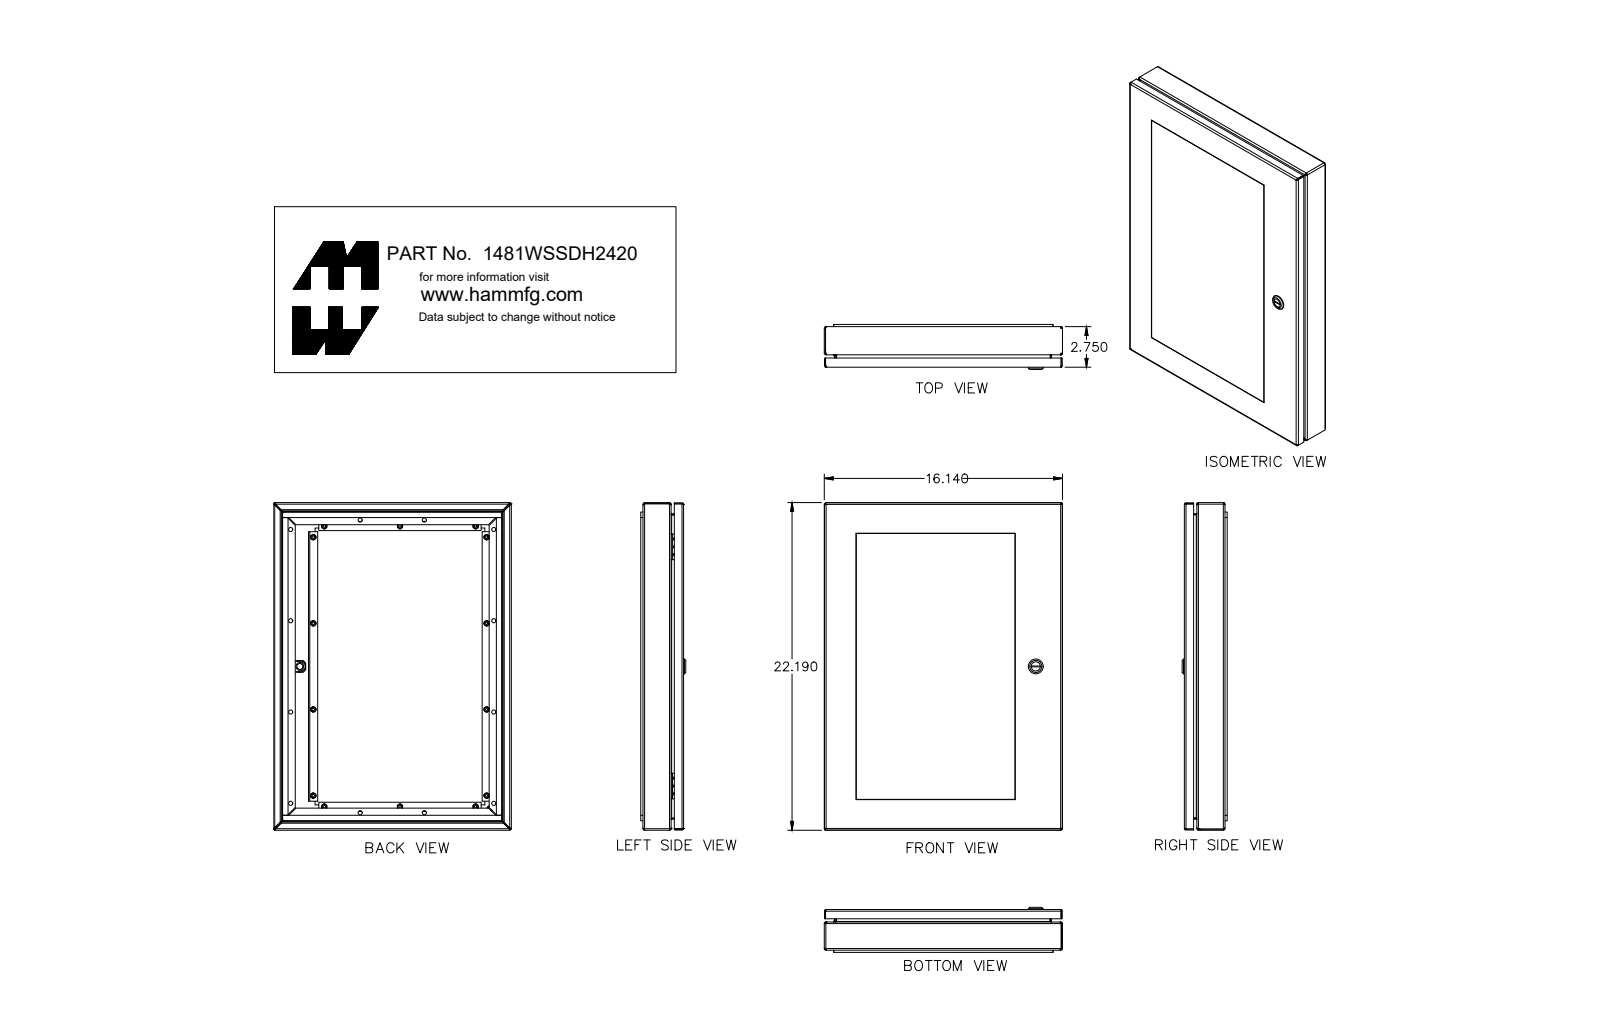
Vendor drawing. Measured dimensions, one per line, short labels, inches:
name: 1481WSSDH2420_Default
written by: SolidWorks 2019 (CONFIG_CONTROL_DESIGN)
unit: in
bodies: 50 solids, 1155 faces (617 planar, 334 cylindrical, 204 other)
size: 22.19 × 16.14 × 2.91
volume: 94.57 in³; area: 1 701 in²
holes: 14× ⌀0.13, 12× ⌀0.281, 2× ⌀0.136, 1× ⌀0.197, 1× ⌀0.24, 1× ⌀0.242, 1× ⌀0.387, 1× ⌀0.5, 1× ⌀0.63, 1× ⌀0.768
bosses: 14× ⌀0.368, 14× ⌀0.226, 14× ⌀0.164, 1× ⌀1.1, 1× ⌀0.785, 1× ⌀0.625, 1× ⌀0.525, 1× ⌀0.477
rounds: 28× R0.036, 28× R0.101, 28× R0.108, 4× R0.016, 4× R0.088, 2× R0.125, 1× R0.021, 1× R0.029
face distances: 0.072, 0.25, 0.178, 2.578, 2.328, 0.842, 1.736, 0.592, 16.068, 2.65
hole spacings: 4.75, 5.833, 6.182, 9.078, 11.026, 11.335, 11.75, 13.119
